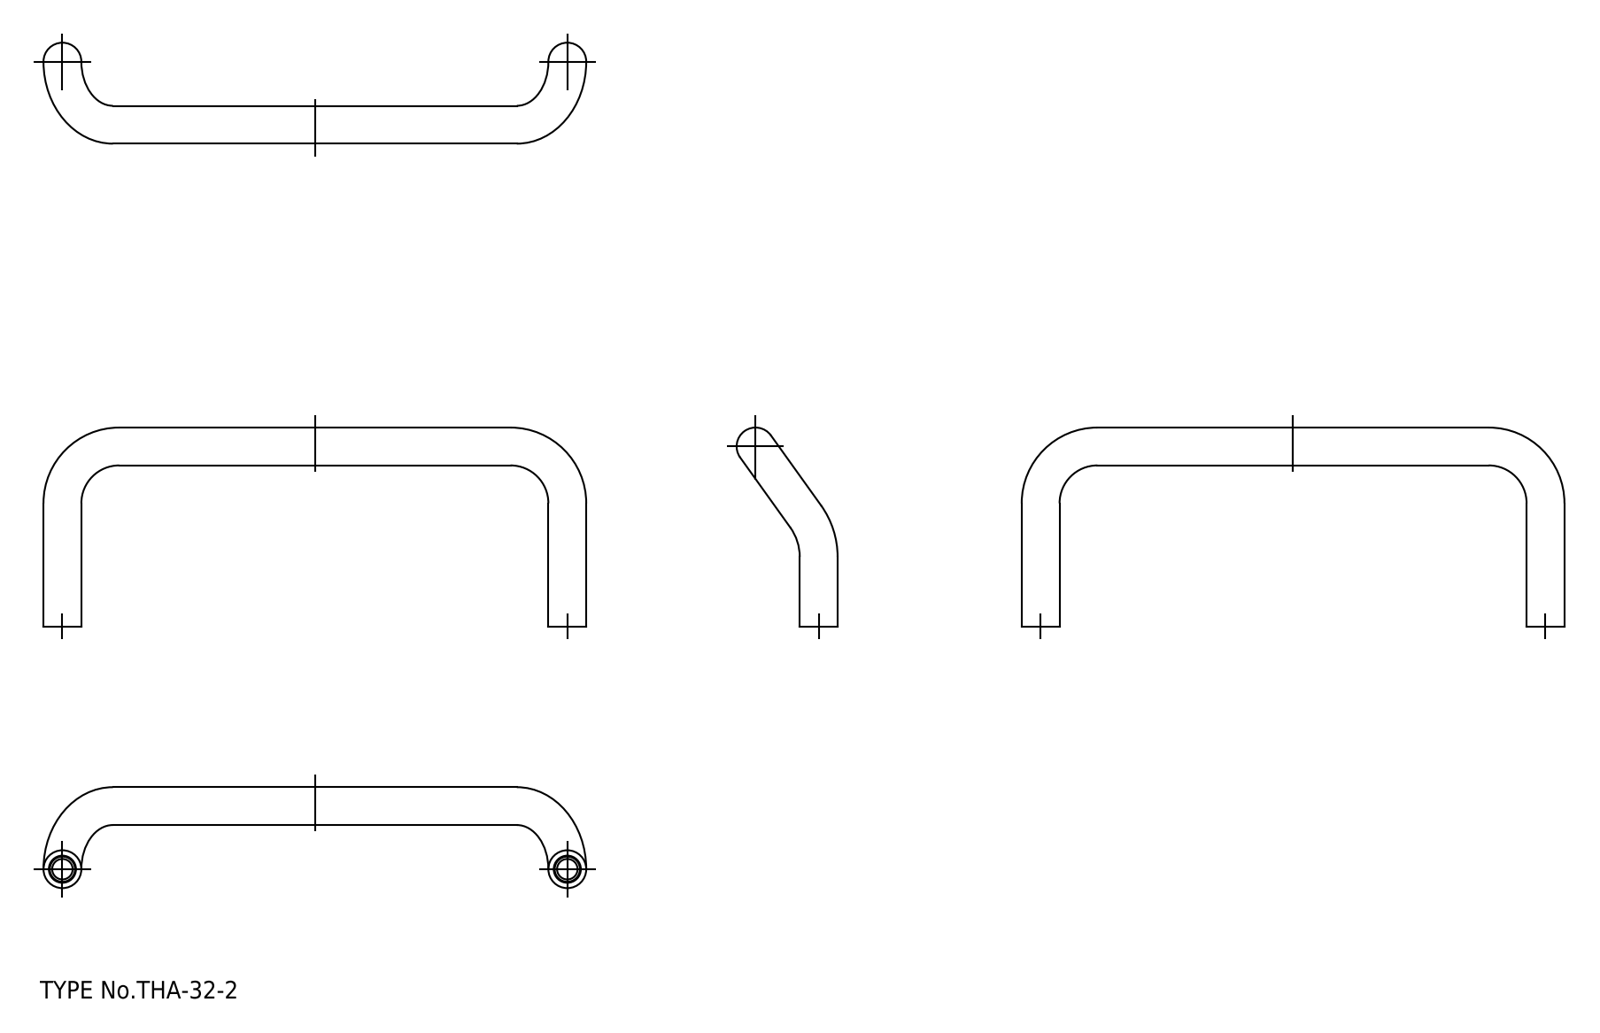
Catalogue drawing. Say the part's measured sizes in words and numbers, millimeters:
Its 3-D file was written by "spGate 17.5.2 (AUTOMOTIVE_DESIGN)". It is 1 solid with 26 faces: 4 planar, 14 cylindrical and 8 other. Overall it measures 86 by 31.5 by 16 millimeters. Its volume is 3 649 cubic millimeters and its surface area 2 783 square millimeters. Round holes: 2 of diameter 4. Round bosses or shafts: 5 of diameter 6. The main face-to-face distances are 7. The hole center spacings are 80.
